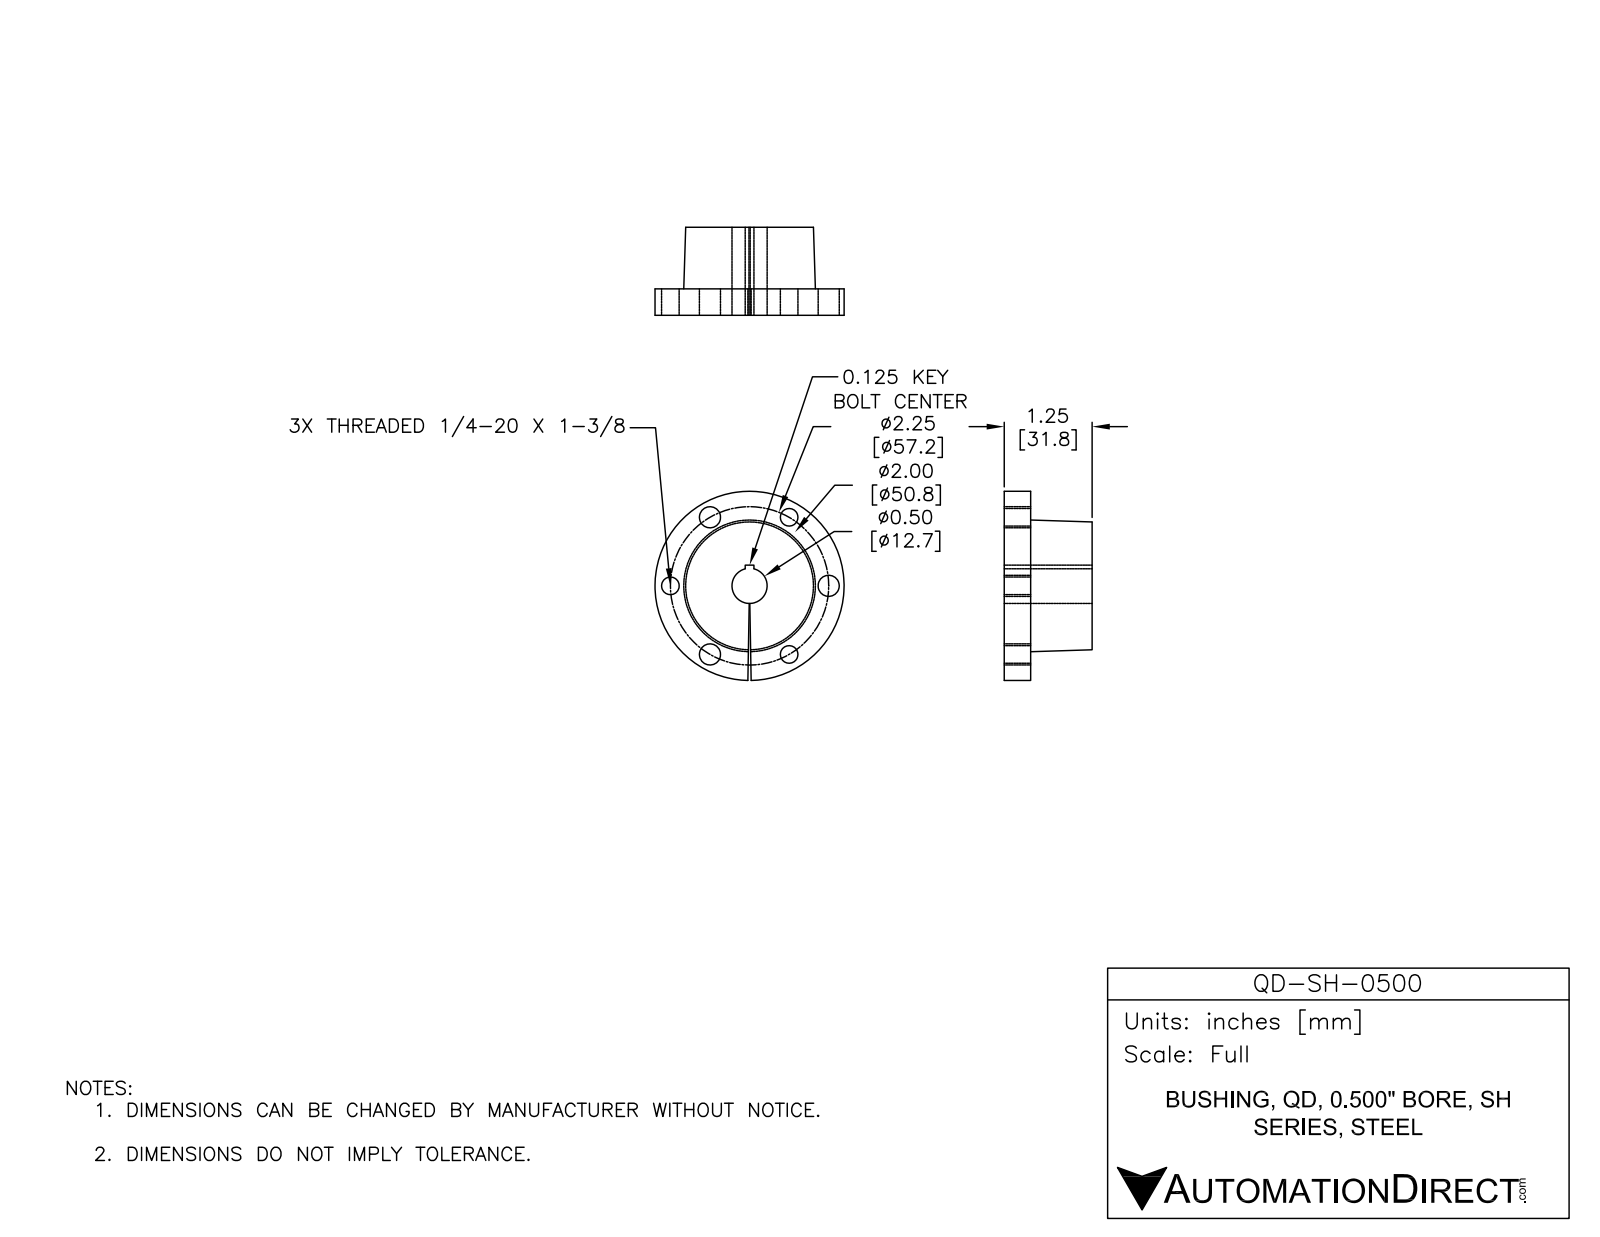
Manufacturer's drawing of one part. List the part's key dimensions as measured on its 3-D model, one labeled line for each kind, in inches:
Part name (STEP PRODUCT): QD-SH-0500
STEP written by: SolidWorks 2014 (AUTOMOTIVE_DESIGN)
Units: inches
Bodies: 1 solid, 29 faces (8 planar, 18 cylindrical, 3 other)
Overall size (bounding box): 2.688 × 2.687 × 1.25
Volume: 4.069 in³ · Surface area: 24.28 in²
Round holes (diameter × count): ⌀0.25 ×3, ⌀0.3 ×3, ⌀0.5 ×1
Round bosses / shafts (diameter × count): ⌀2.687 ×1
Main face-to-face distances: 0.375, 1.25, 0.875, 0.125
Hole centre spacings: 1.125, 1.125, 1.948, 1.949, 2.25, 2.25
